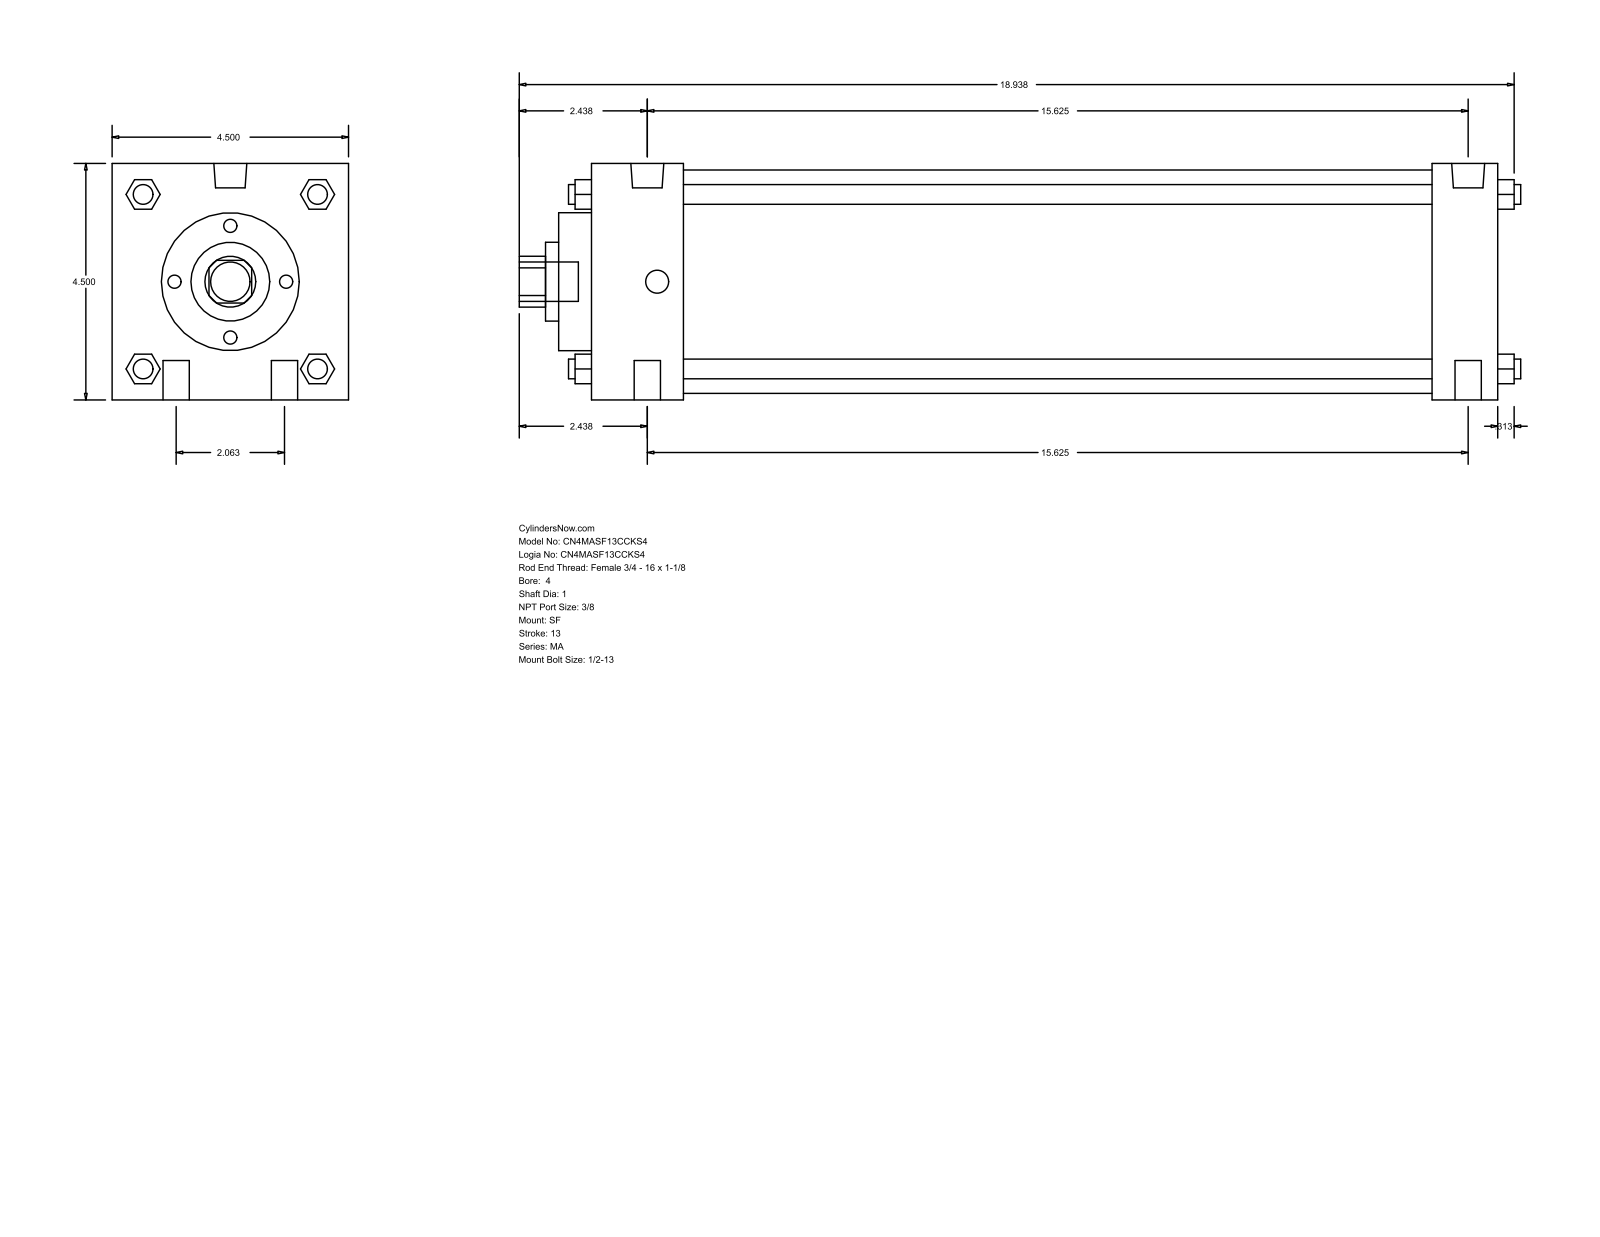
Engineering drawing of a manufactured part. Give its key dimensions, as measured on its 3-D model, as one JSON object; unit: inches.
{"part_name": "MA_SF__0400_1", "step_written_by": "GSSL Pune (CONFIG_CONTROL_DESIGN)", "units": "inches", "bodies": {"solids": 0, "faces": 126, "planar": 95, "cylindrical": 31, "other": 0}, "overall_size": [19.063, 4.5, 4.5], "round_holes": [[1, 1], [1.5, 1], [2.625, 1], [4.25, 1]], "round_bosses_or_shafts": [[0.5, 4], [0.375, 4], [0.627, 2], [0.437, 2], [0.75, 1]], "partial_cylinders_radius": [[0.484, 1]], "face_to_face_distances": [4.5, 17.25, 16, 1.25, 1.75, 14.25, 15.5, 17.875, 0.625, 2.375]}
